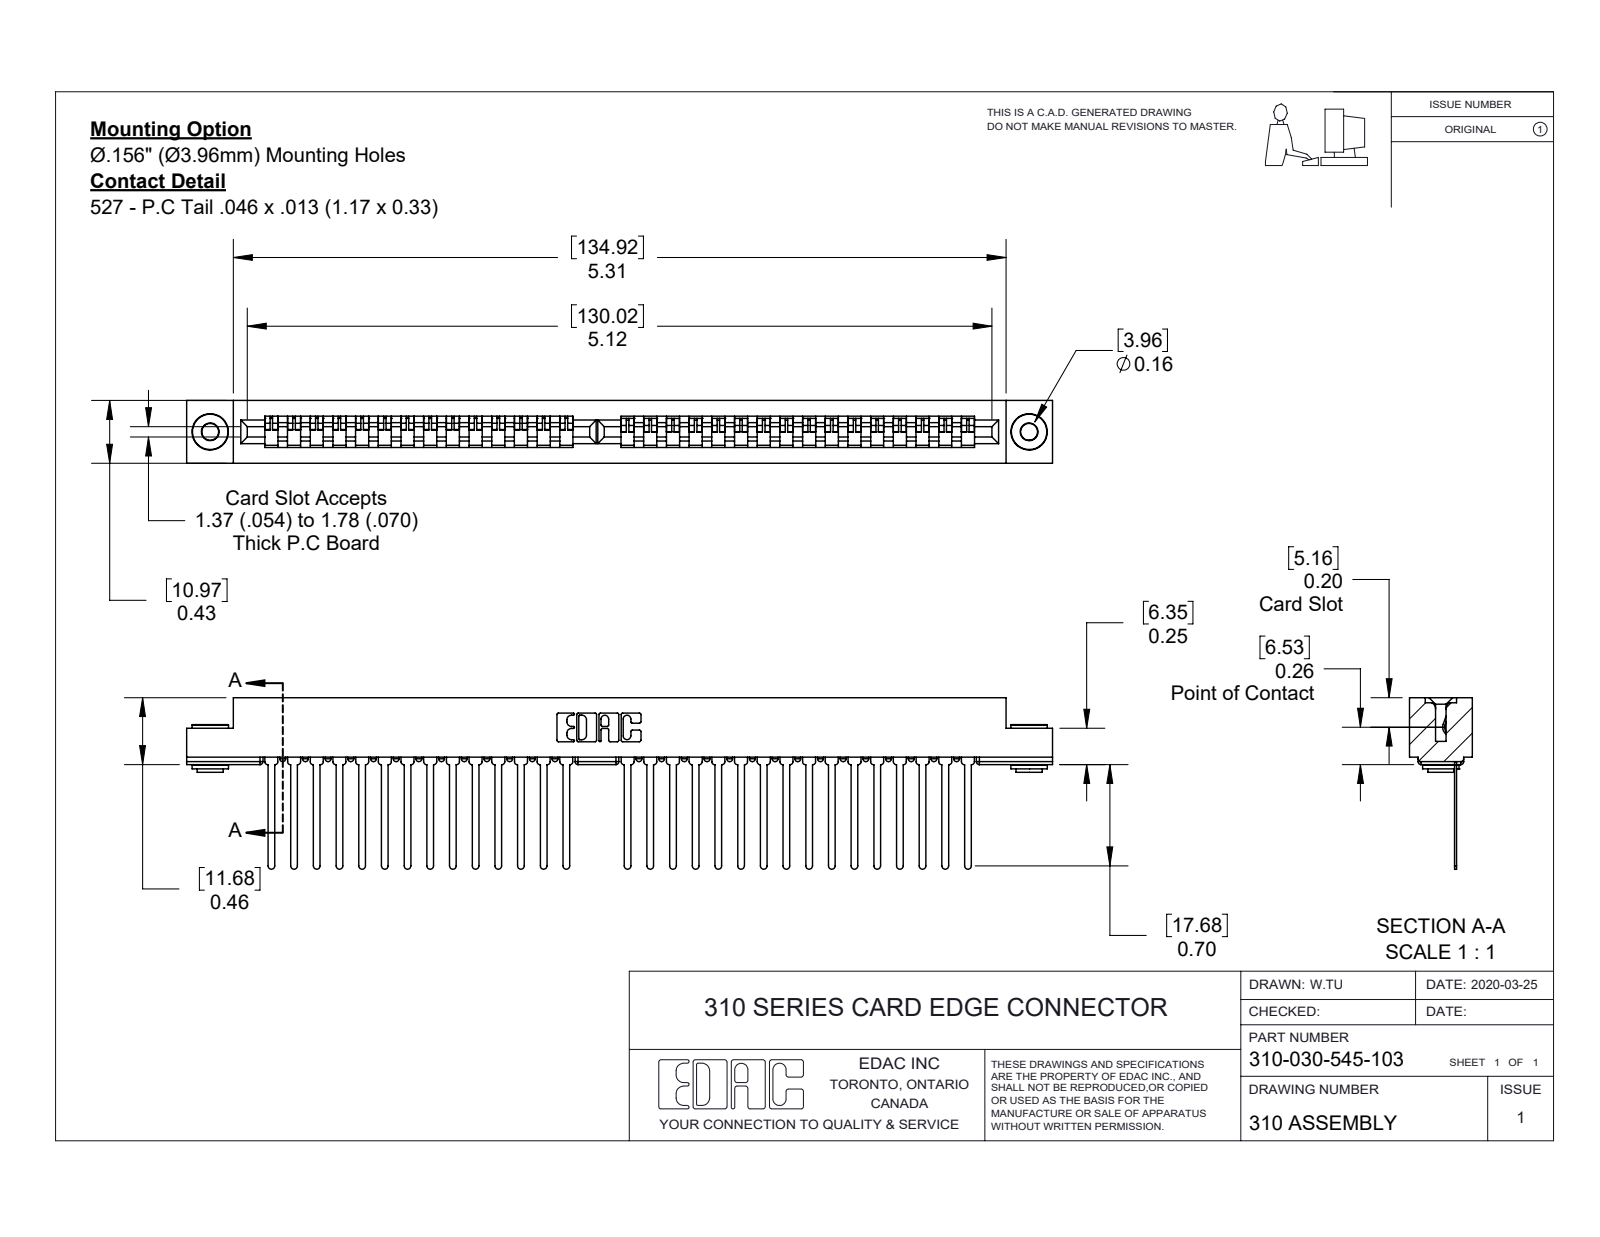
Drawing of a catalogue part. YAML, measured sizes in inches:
part_name: "310-030-545-103; 307-290-001_545; 345-250-002_345-250-002-102; 310 Part_.116 Hex"
step_written_by: "SolidWorks 2016 (CONFIG_CONTROL_DESIGN)"
units: inches
bodies: {solids: 33, faces: 1898, planar: 1218, cylindrical: 608, other: 72}
overall_size: [5.953, 1.179, 0.432]
volume: 0.781
surface_area: 25.14
round_holes:
  - {diameter: 0.116, count: 2}
  - {diameter: 0.156, count: 2}
round_bosses_or_shafts:
  - {diameter: 0.25, count: 2}
  - {diameter: 0.18, count: 2}
  - {diameter: 0.136, count: 2}
partial_cylinders:
  - {radius: 0.02, count: 158}
  - {radius: 0.023, count: 30}
  - {radius: 0.01, count: 22}
  - {radius: 0.007, count: 6}
  - {radius: 0.031, count: 6}
  - {radius: 0.026, count: 3}
  - {radius: 0.012, count: 2}
  - {radius: 0.025, count: 2}
face_to_face_distances: [0.109, 0.324, 0.015, 0.013, 0.432, 0.072, 0.124, 0.309, 0.2, 0.409]
hole_center_spacings: [5.63]
